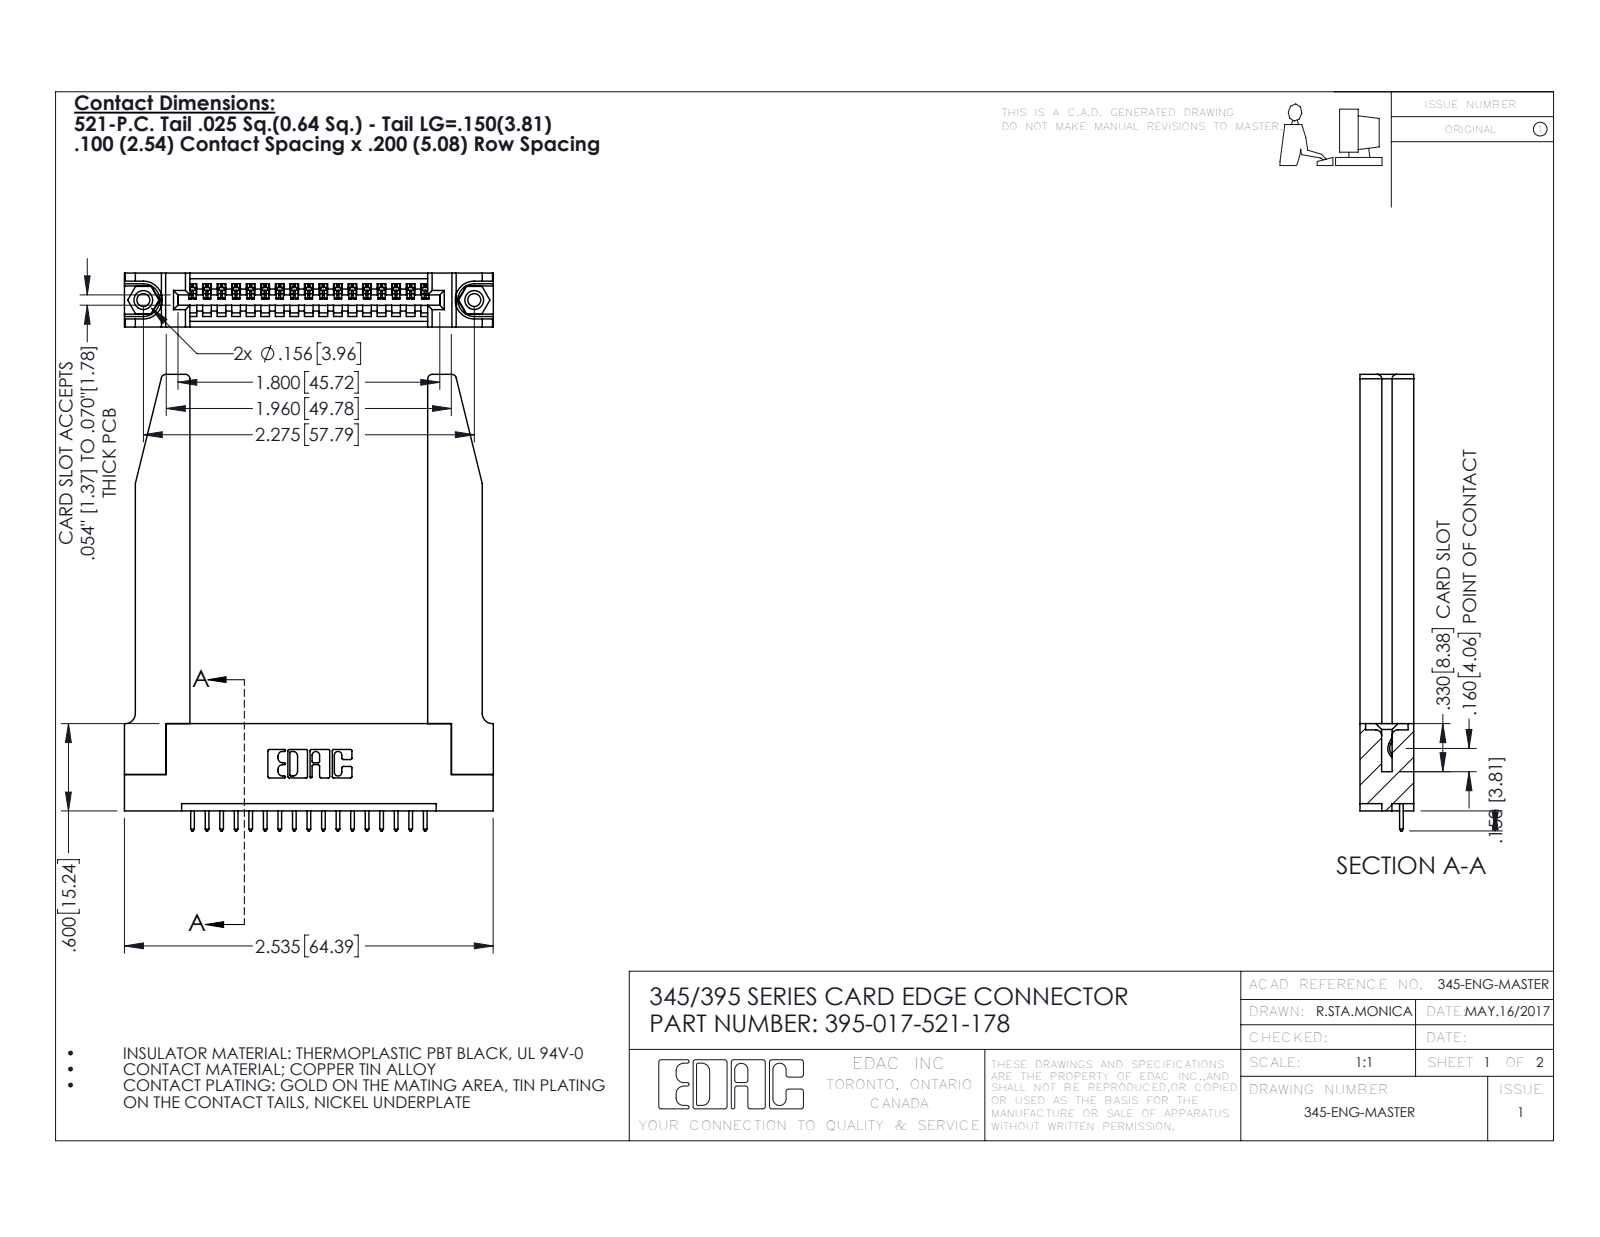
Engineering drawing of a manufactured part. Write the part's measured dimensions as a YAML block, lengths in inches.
part_name: "345-220-078_345-220-078; 345-250-001_345-250-001-102; 345-292-001_345-293-121; 395-017-521-178 (+1 more)"
step_written_by: "SolidWorks 2016 (CONFIG_CONTROL_DESIGN)"
units: inches
bodies: {solids: 22, faces: 1346, planar: 902, cylindrical: 392, other: 52}
overall_size: [3.137, 2.536, 0.37]
volume: 0.832
surface_area: 21.87
round_holes:
  - {diameter: 0.089, count: 2}
  - {diameter: 0.125, count: 2}
  - {diameter: 0.156, count: 2}
  - {diameter: 0.064, count: 1}
round_bosses_or_shafts:
  - {diameter: 0.155, count: 2}
partial_cylinders:
  - {radius: 0.006, count: 34}
  - {radius: 0.01, count: 34}
  - {radius: 0.01, count: 22}
  - {radius: 0.03, count: 8}
  - {radius: 0.007, count: 6}
  - {radius: 0.031, count: 6}
  - {radius: 0.026, count: 3}
  - {radius: 0.031, count: 2}
face_to_face_distances: [0.37, 0.072, 0.298, 0.2, 0.148, 0.15, 0.098, 0.272, 0.025, 0.077]
hole_center_spacings: [0.27, 2.041, 2.275]
